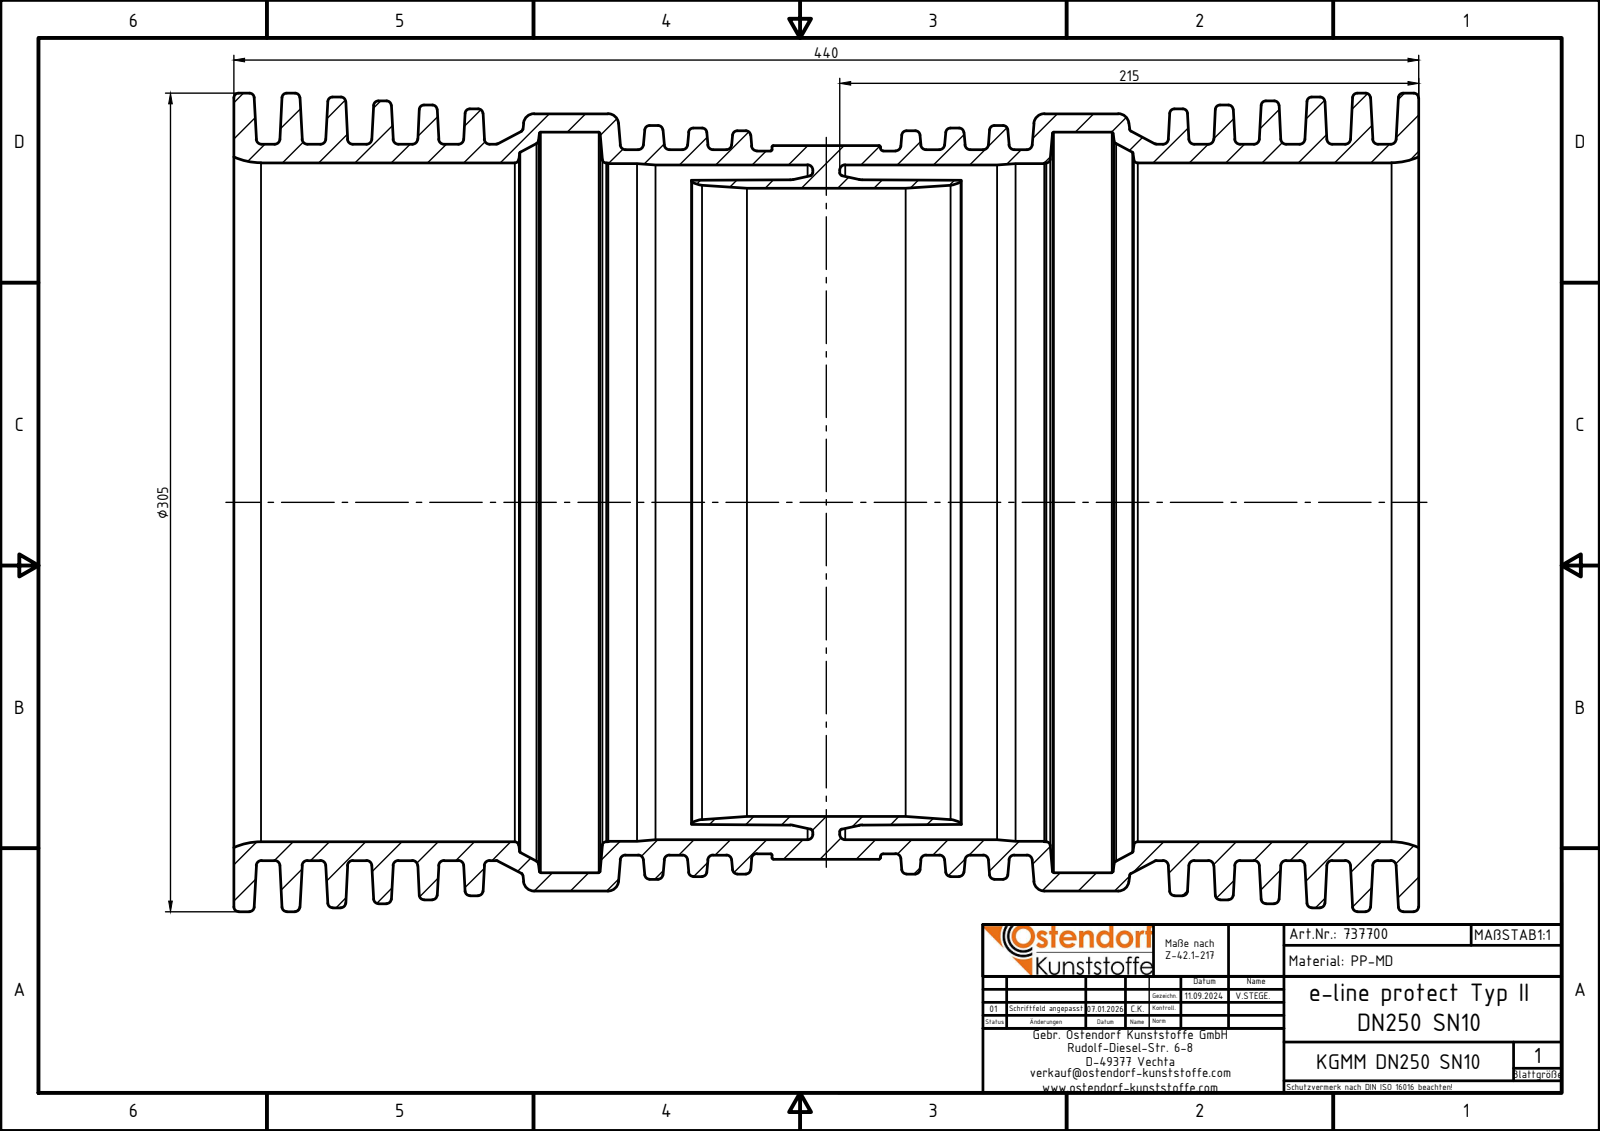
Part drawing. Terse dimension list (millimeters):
name: 737700z
written by: Autodesk Inventor 2024 (AUTOMOTIVE_DESIGN)
unit: mm
bodies: 1 solid, 226 faces (8 planar, 52 cylindrical, 166 other)
size: 439.94 × 303.93 × 303.93
volume: 4 445 000 mm³; area: 1 309 000 mm²
holes: 1× ⌀233.22, 1× ⌀250.51, 1× ⌀251.54, 1× ⌀251.98, 1× ⌀274.96
bosses: 1× ⌀303.93, 1× ⌀300.98, 1× ⌀298.04, 1× ⌀295.09, 1× ⌀292.14, 1× ⌀288.51, 1× ⌀279.87, 1× ⌀277.91
face distances: 439.94, 214.96, 224.98, 199.84, 240.1, 15.12, 25.14, 10.02, 40.26, 169.89
